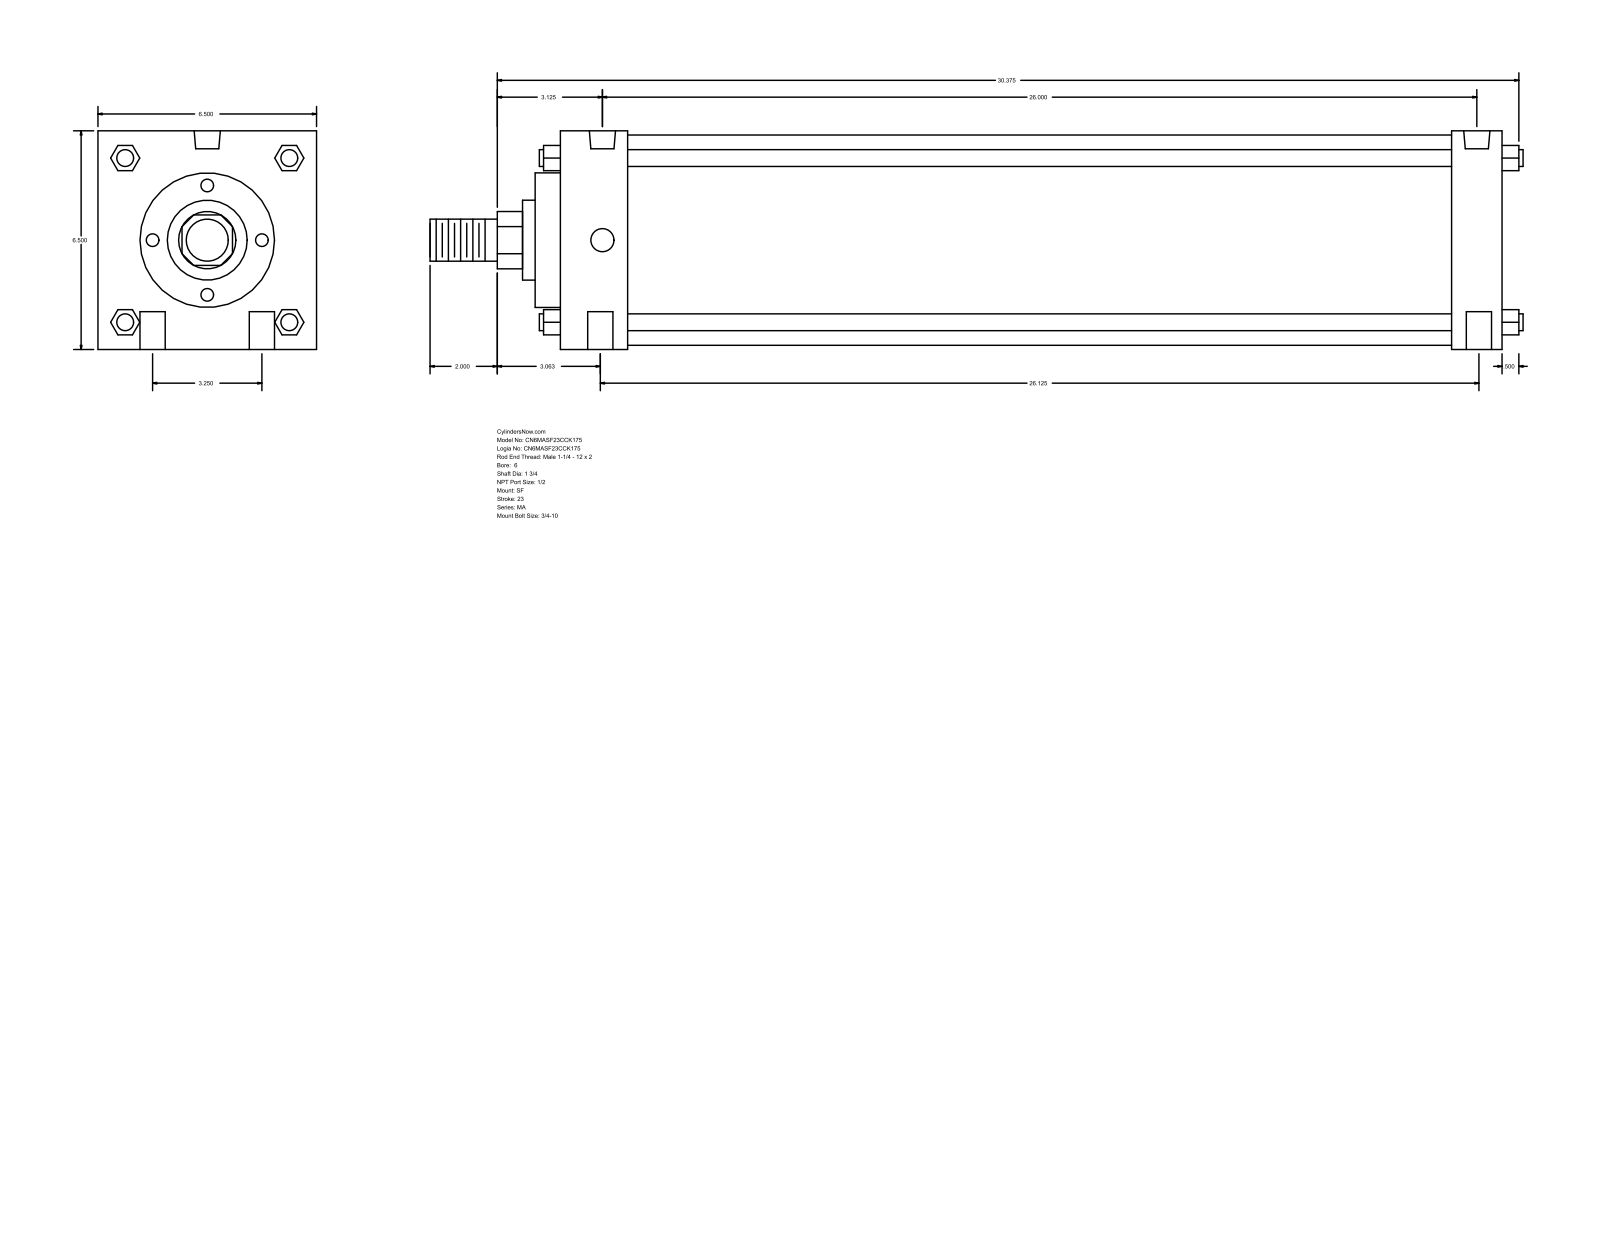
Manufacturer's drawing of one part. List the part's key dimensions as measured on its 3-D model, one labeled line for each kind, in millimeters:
Part name (STEP PRODUCT): MA_SF__0600_1.75
STEP written by: GSSL Pune (CONFIG_CONTROL_DESIGN)
Units: millimetres
Bodies: 0 solids, 126 faces (95 planar, 31 cylindrical, 0 other)
Overall size (bounding box): 825.5 × 165.1 × 165.1
Round holes (diameter × count): ⌀19.05 ×4, ⌀17.46 ×2, ⌀19.77 ×2
Round bosses / shafts (diameter × count): ⌀12.7 ×4, ⌀158.75 ×1, ⌀101.6 ×1, ⌀60.33 ×1, ⌀44.45 ×1, ⌀31.75 ×1
Partial cylindrical surfaces — rounded edges, fillets, slot ends (radius × count): R21.63 ×1
Main face-to-face distances: 165.1, 711.21, 19.05, 50.8, 38.1, 673.11, 622.31, 660.41, 69.85, 692.16
Hole centre spacings: 41.3, 663.27, 82.54, 660.39, 663.57, 668.68
